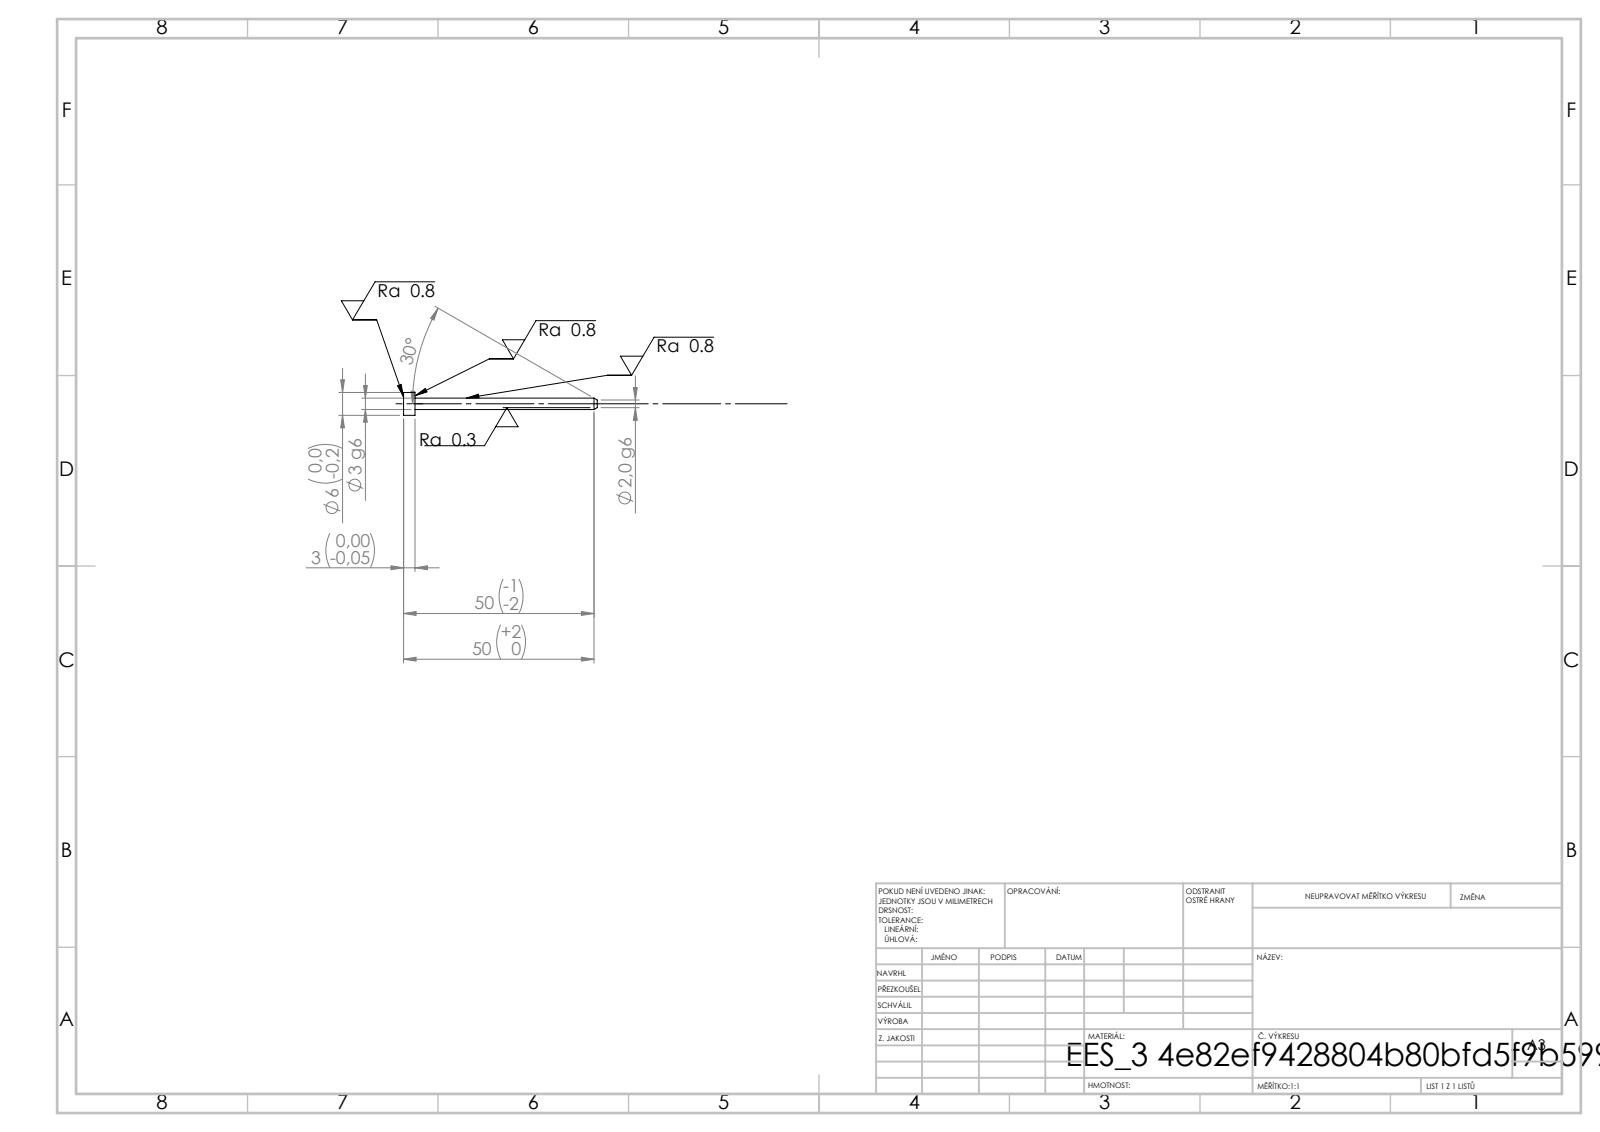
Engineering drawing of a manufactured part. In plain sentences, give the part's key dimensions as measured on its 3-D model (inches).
Its 3-D file was written by "SolidWorks 2019 (CONFIG_CONTROL_DESIGN)". It is 1 solid with 11 faces: 3 planar, 6 cylindrical and 2 other. Overall it measures 2.003 by 0.236 by 0.236 inches. Its volume is 0.026 cubic inches and its surface area 0.876 square inches. Round holes: 1 of diameter 0.079. Round bosses or shafts: 1 of diameter 0.236, 1 of diameter 0.118. The main face-to-face distances are 0.118, 1.85, 1.969.
